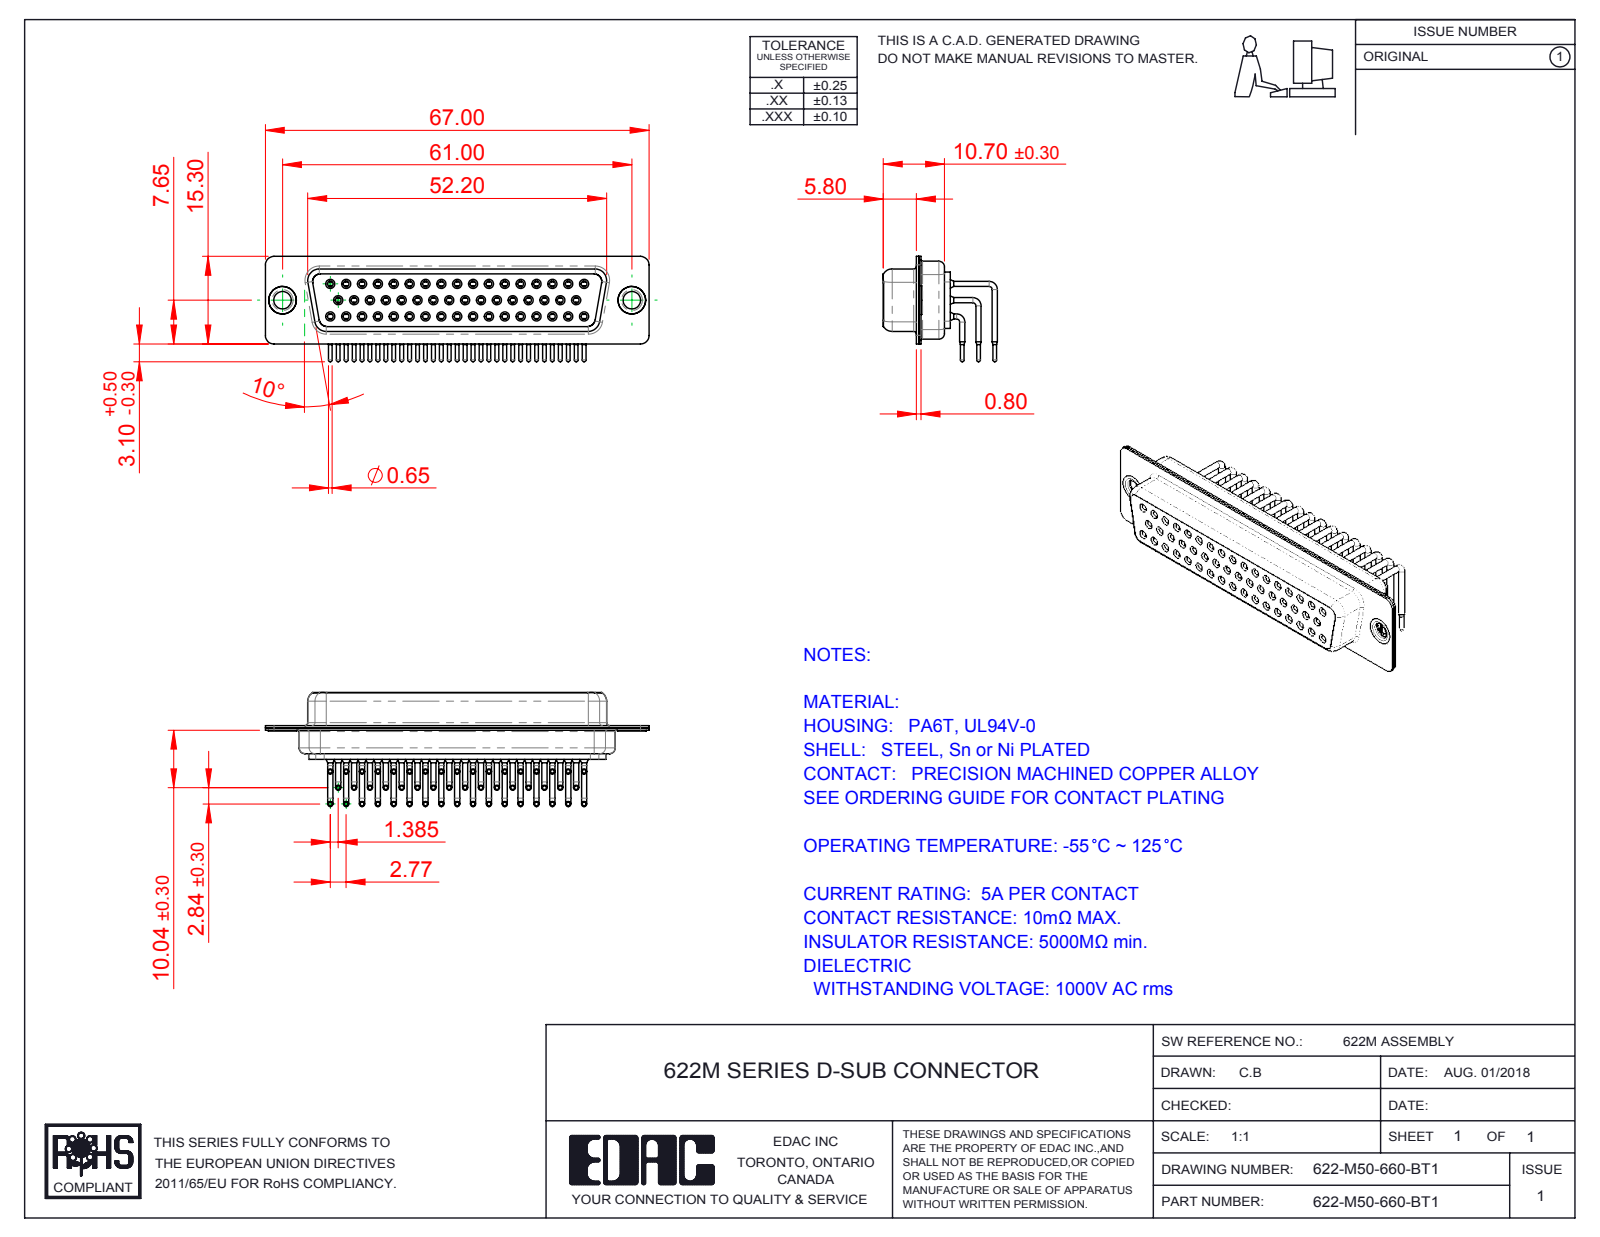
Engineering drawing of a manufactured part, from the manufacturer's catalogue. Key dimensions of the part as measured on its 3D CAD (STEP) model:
Part name (STEP PRODUCT): 622M Shell Rear_50 Contacts; 622M Thru Hole Rivet; 622-M50-660-BT1; 622M Contact Row 2_50 Contacts (+4 more)
STEP written by: SolidWorks 2016 (CONFIG_CONTROL_DESIGN)
Units: millimetres
Bodies: 55 solids, 2903 faces (817 planar, 1271 cylindrical, 815 other)
Overall size (bounding box): 67 × 19.93 × 18.4
Volume: 6 854 mm³ · Surface area: 15 982 mm²
Round holes (diameter × count): ⌀1 ×50, ⌀1.1 ×50, ⌀1.7 ×50, ⌀1.8 ×50, ⌀2 ×50, ⌀3.05 ×2, ⌀4 ×2, ⌀4.8 ×2
Round bosses / shafts (diameter × count): ⌀0.9 ×100, ⌀1.6 ×50, ⌀1.5 ×50, ⌀0.65 ×50, ⌀5 ×2, ⌀4.9 ×2, ⌀3.55 ×2
Partial cylindrical surfaces — rounded edges, fillets, slot ends (radius × count): R1.5 ×16, R2 ×12, R1.35 ×8, R1.6 ×8, R0.25 ×4, R0.5 ×4, R0.6 ×4, R0.65 ×4
Main face-to-face distances: 0.4, 1.35, 11.85, 0.85, 2.2, 5.5, 12.25, 5.9, 10.5, 10.05
Hole centre spacings: 2.77, 3.16, 5.54, 8.31, 11.08, 13.85, 16.62, 19.39
